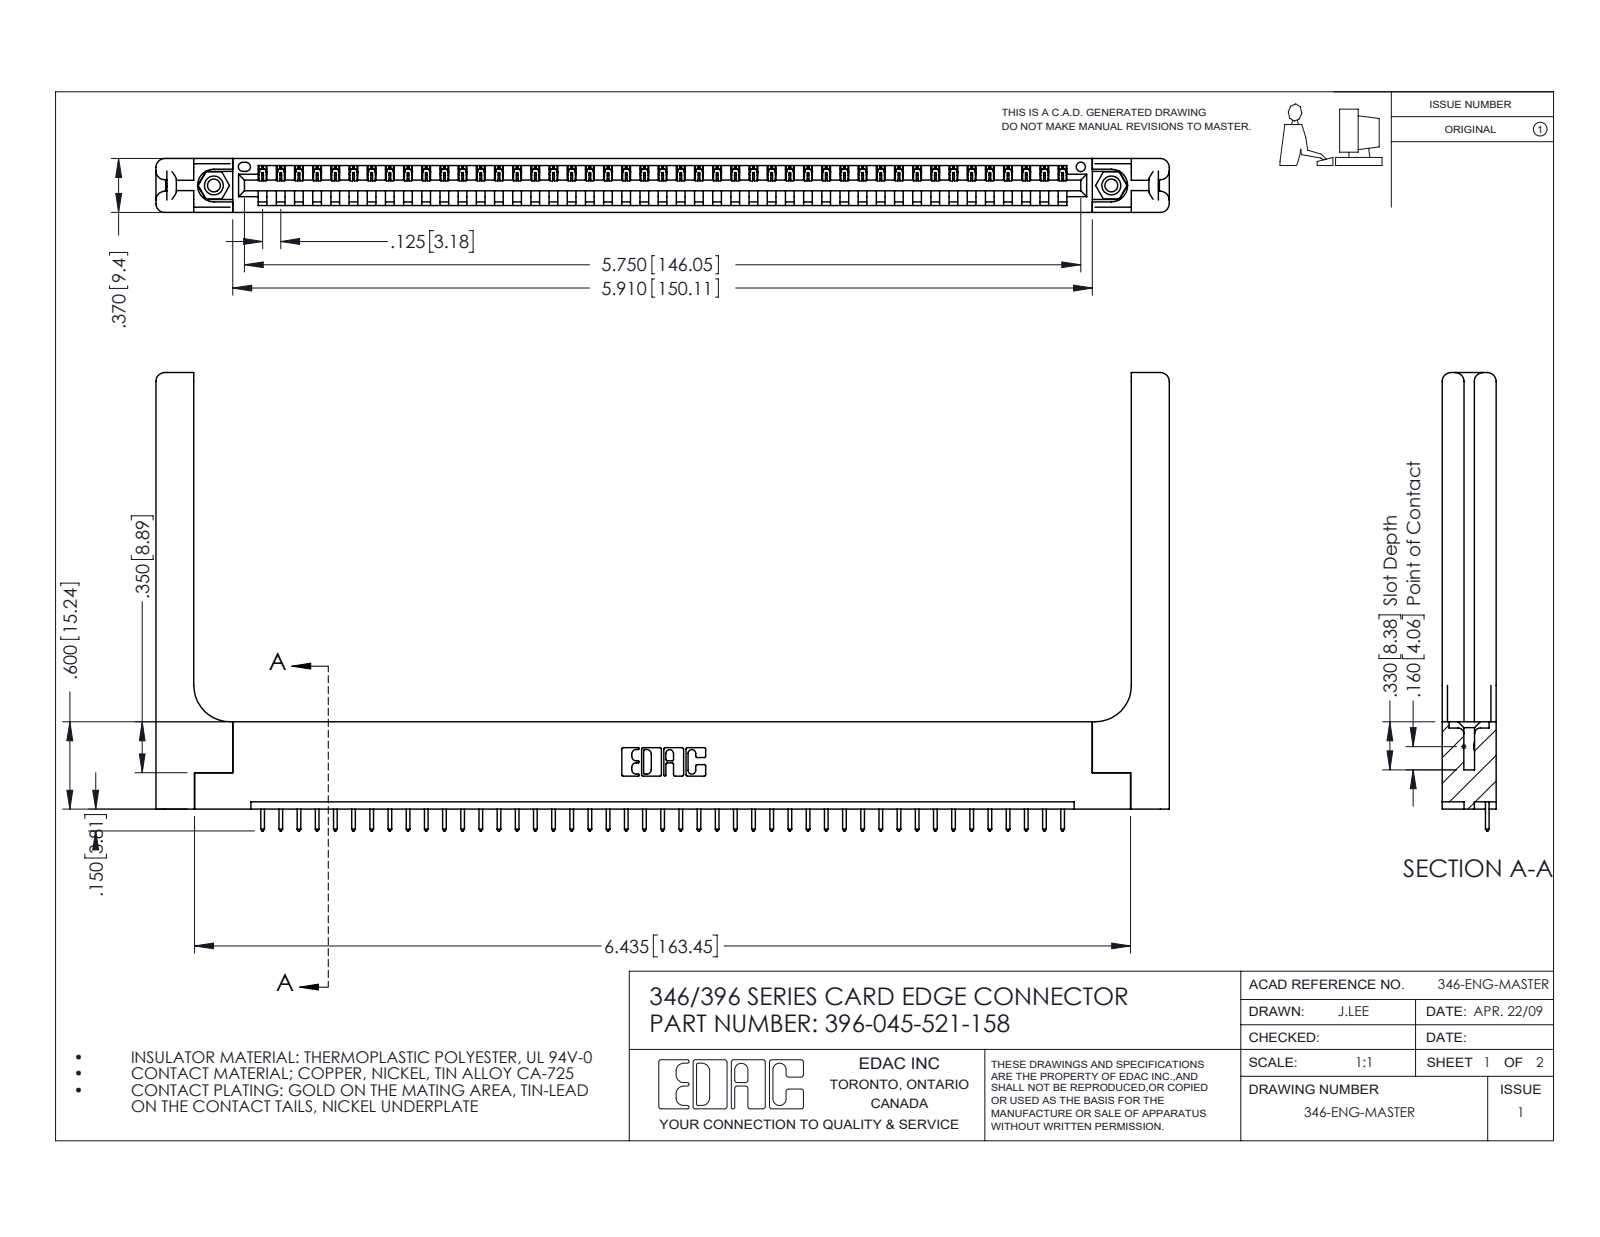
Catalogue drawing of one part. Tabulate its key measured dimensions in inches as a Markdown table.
| quantity | value |
| --- | --- |
| part name | 396-045-521-158; 346-220-058_345-220-058; 345-292-001_345-293-121; 345-250-001_345-250-001-102 (+1 more) |
| STEP written by | SolidWorks 2016 (CONFIG_CONTROL_DESIGN) |
| units | inches |
| bodies | 50 solids, 2988 faces (2024 planar, 904 cylindrical, 60 other) |
| overall size | 6.966 × 3.15 × 0.37 |
| volume | 1.486 in³ |
| surface area | 39.88 in² |
| round holes (diameter × count) | 0.089 × 2, 0.125 × 2, 0.156 × 2, 0.064 × 1 |
| round bosses / shafts (diameter × count) | 0.155 × 2 |
| partial cylindrical surfaces (radius × count) | 0.006 × 90, 0.01 × 90, 0.01 × 22, 0.06 × 16, 0.007 × 6, 0.031 × 6, 0.026 × 3, 0.03 × 2 |
| main face-to-face distances | 0.37, 0.048, 0.322, 0.072, 0.148, 0.15, 0.25, 0.298, 0.025, 0.222 |
| hole center spacings | 0.246, 5.961, 6.17 |
